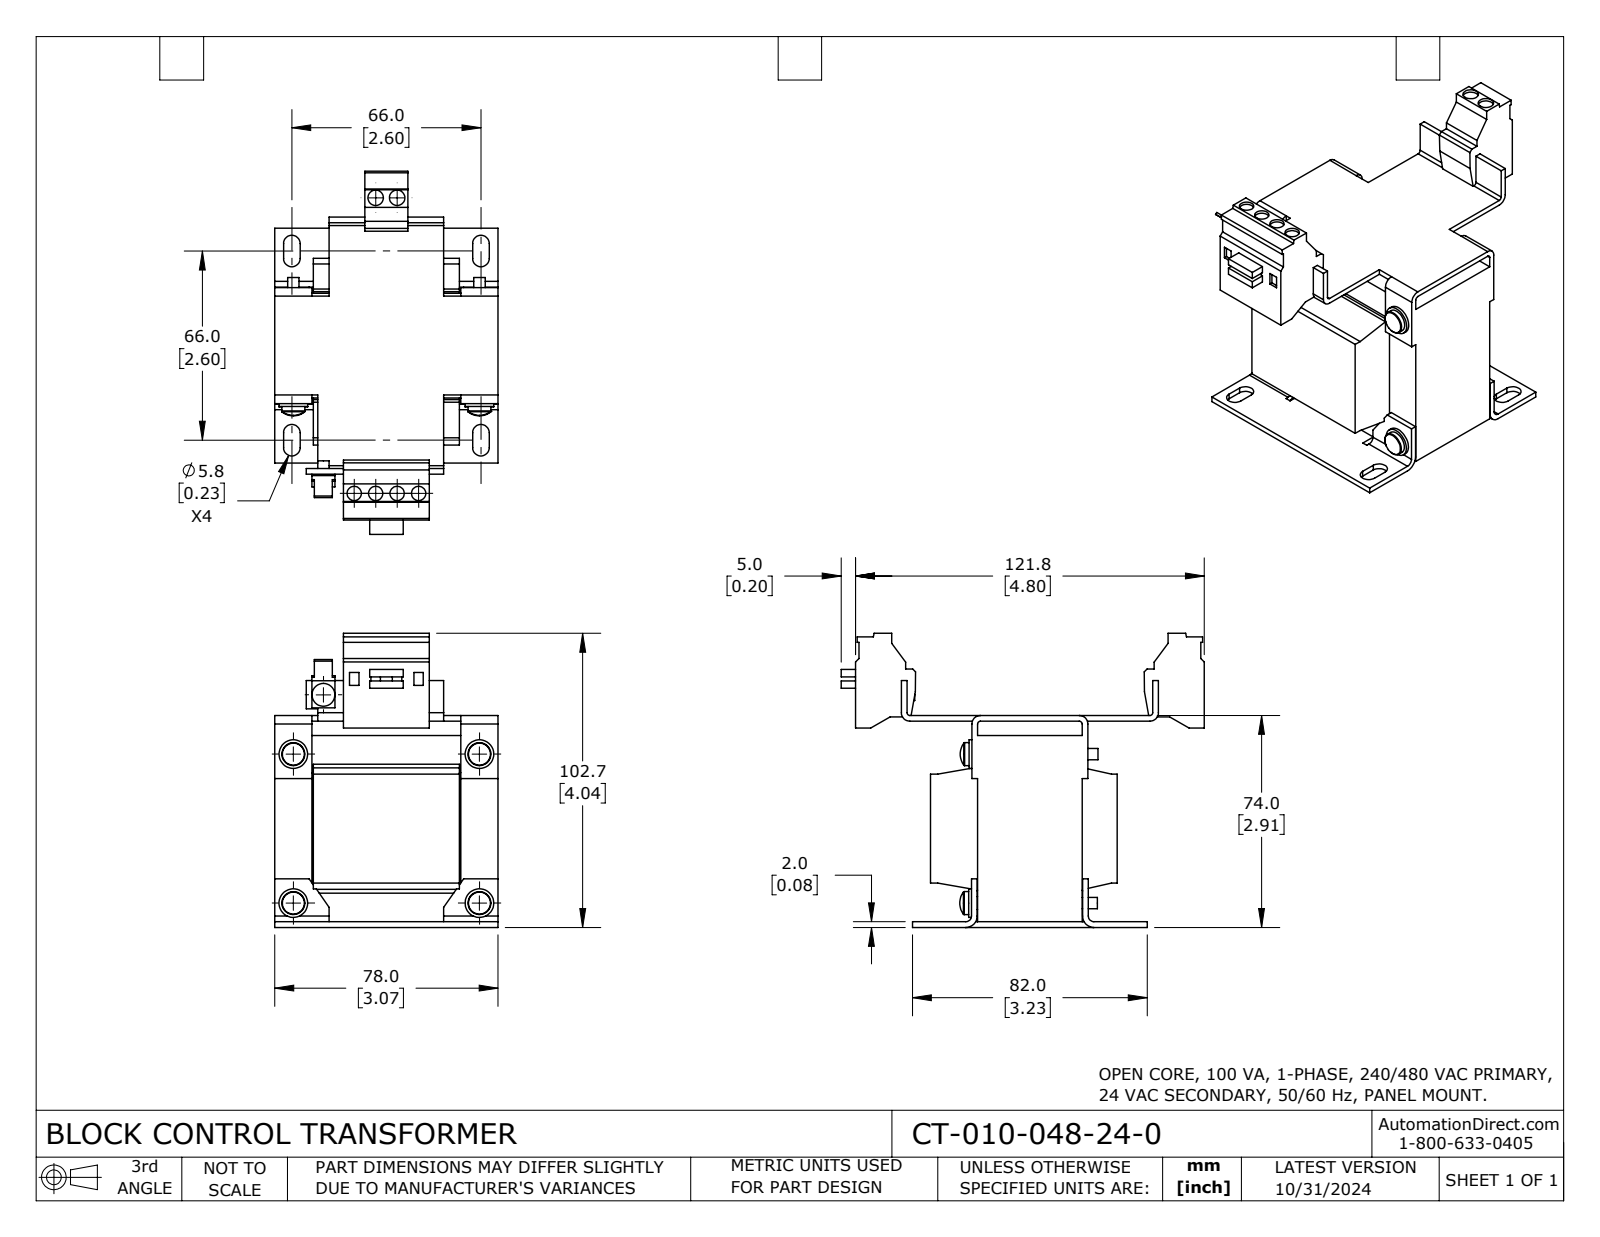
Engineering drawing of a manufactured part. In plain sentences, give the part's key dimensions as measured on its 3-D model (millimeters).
The part is named "CT-010-048-24-0". Its 3-D file was written by "SolidWorks 2023 (CONFIG_CONTROL_DESIGN)". It is 1 solid with 337 faces: 245 planar, 80 cylindrical and 12 other. Overall it measures 126.8 by 102.7 by 78 millimeters. Its volume is 291 700 cubic millimeters and its surface area 64 970 square millimeters. Round holes: 4 of diameter 5, 2 of diameter 5.4. Round bosses or shafts: 5 of diameter 8, 5 of diameter 4, 4 of diameter 10, 2 of diameter 4.5. Partial cylindrical surfaces (rounded edges, fillets, slot ends): 8 of radius 2.9, 4 of radius 1, 4 of radius 3, 2 of radius 2, 2 of radius 4. The main face-to-face distances are 2, 72, 13.5, 65, 51.5, 0.5, 64.5, 13, 70, 74. The hole center spacings are 7.5, 103.5, 15, 103.2, 104.3, 22.5.
